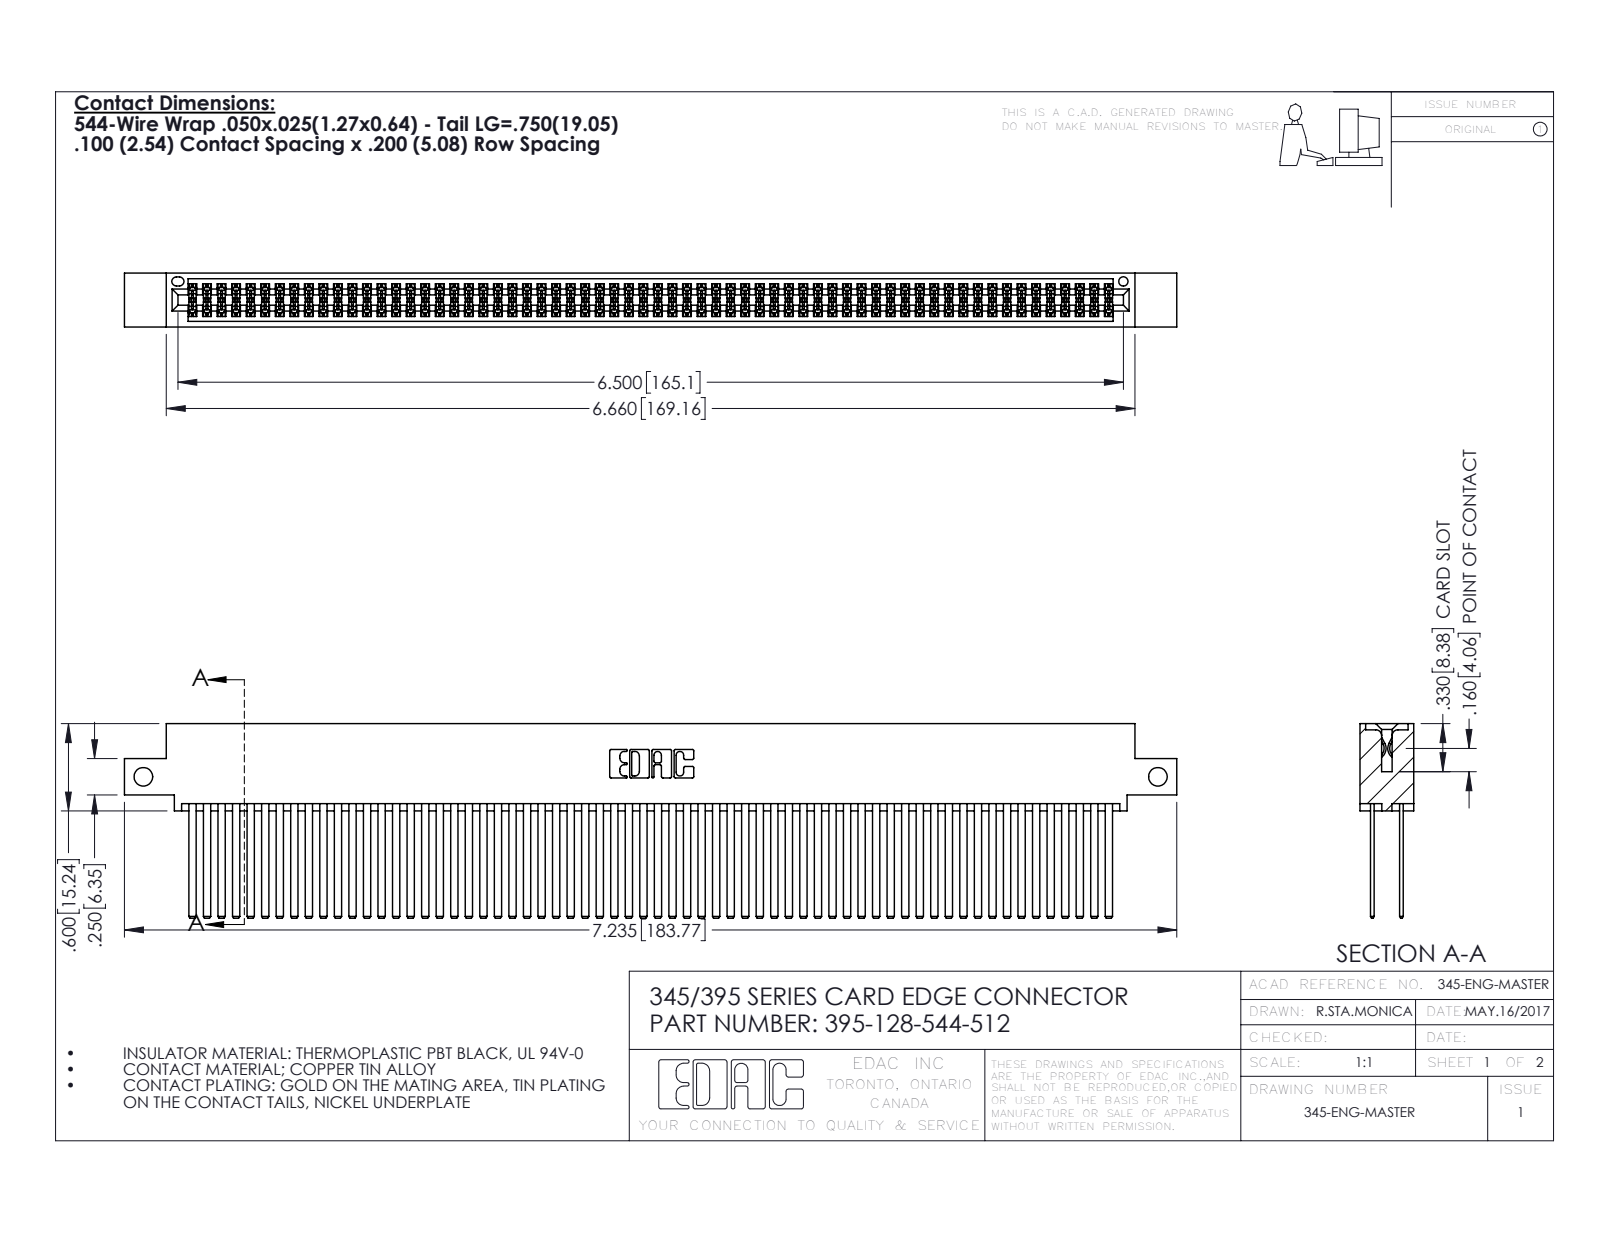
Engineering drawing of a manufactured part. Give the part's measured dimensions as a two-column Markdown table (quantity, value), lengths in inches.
| quantity | value |
| --- | --- |
| part name | 395-128-544-512; 345-292-001_345-293-144; 345 Part_0.110 Offset - Side Mount |
| STEP written by | SolidWorks 2016 (CONFIG_CONTROL_DESIGN) |
| units | inches |
| bodies | 129 solids, 5762 faces (3796 planar, 1966 cylindrical, 0 other) |
| overall size | 7.235 × 1.337 × 0.37 |
| volume | 1.202 in³ |
| surface area | 53.86 in² |
| round holes (diameter × count) | 0.128 × 2, 0.064 × 1 |
| partial cylindrical surfaces (radius × count) | 0.006 × 192, 0.01 × 22, 0.007 × 6, 0.031 × 6, 0.026 × 3, 0.014 × 2, 0.019 × 2, 0.022 × 2 |
| main face-to-face distances | 0.2, 0.025, 0.298, 0.072, 0.098, 0.272, 0.225, 0.175, 0.37, 0.149 |
| hole center spacings | 6.975 |
